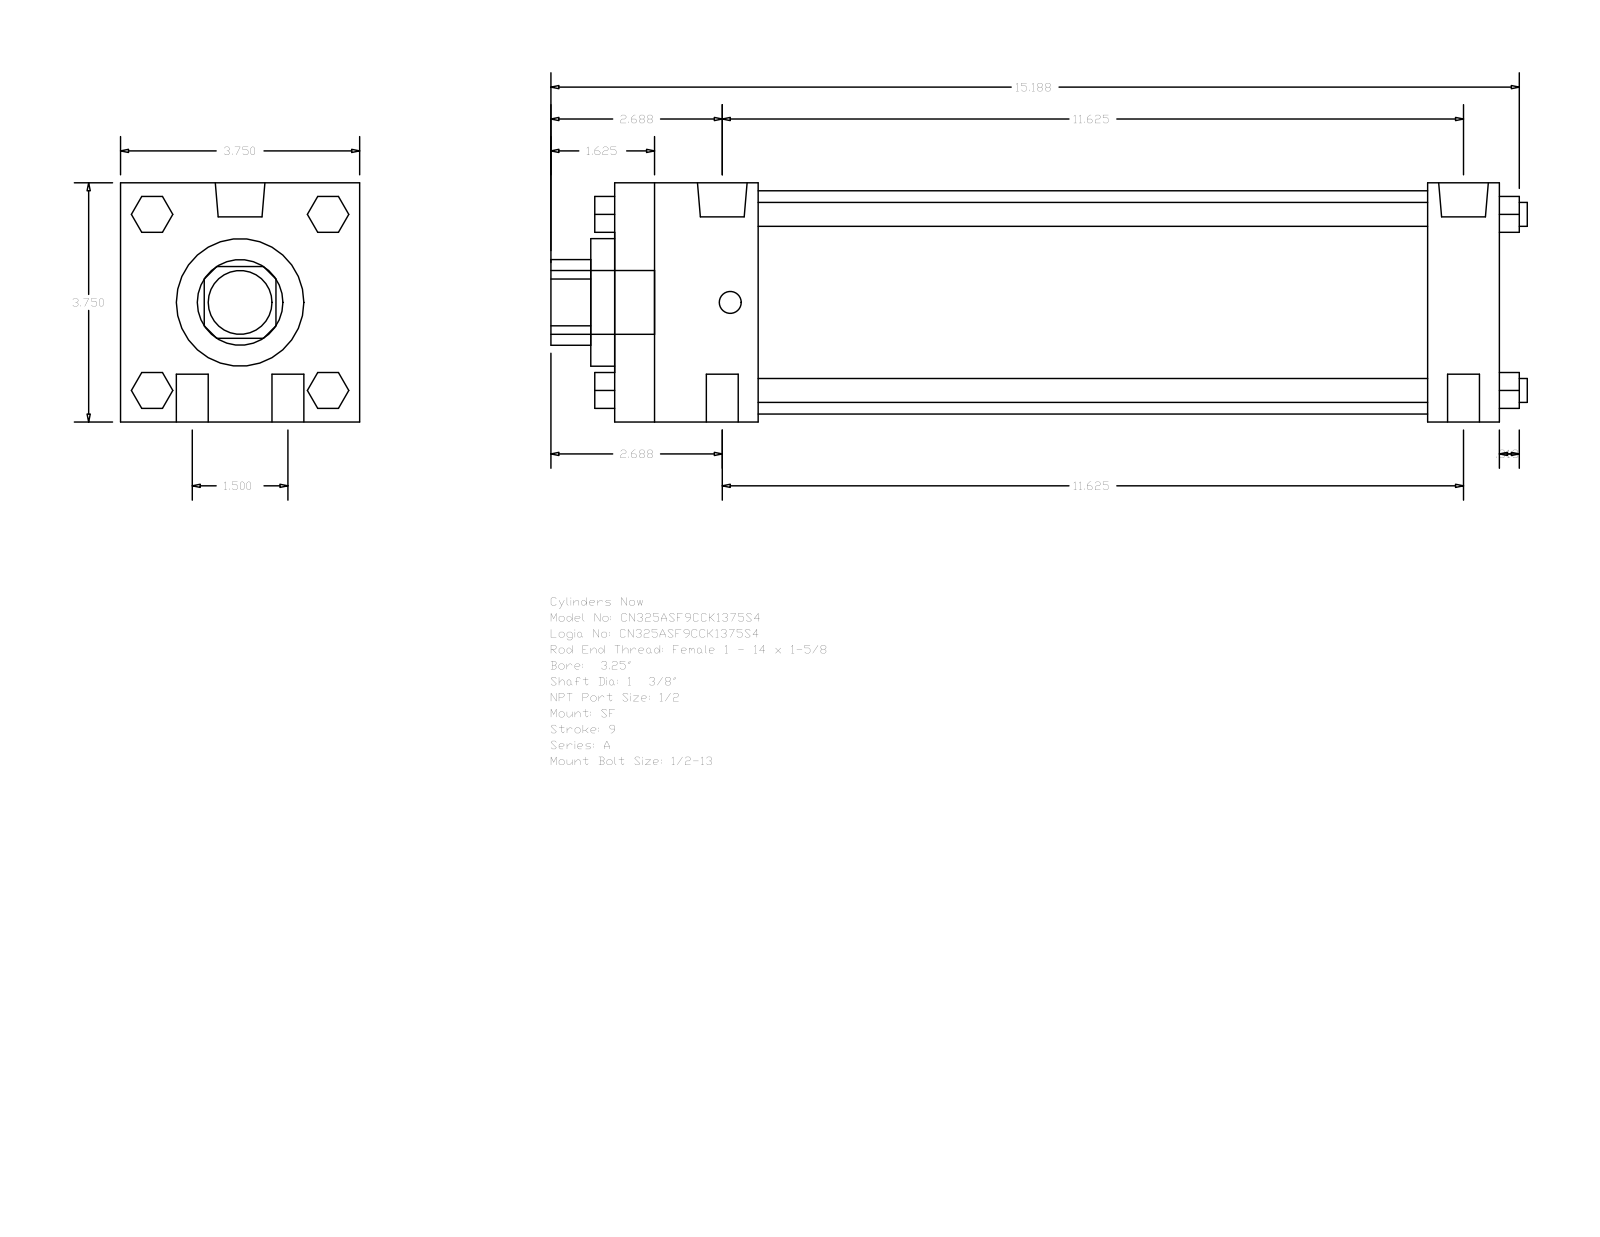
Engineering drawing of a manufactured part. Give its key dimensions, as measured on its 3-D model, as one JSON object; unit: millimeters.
{"part_name": "A_SF__0325_1.375", "step_written_by": "GSSL Pune (CONFIG_CONTROL_DESIGN)", "units": "millimeters", "bodies": {"solids": 0, "faces": 124, "planar": 94, "cylindrical": 30, "other": 0}, "overall_size": [388.94, 95.25, 95.25], "round_holes": [[34.92, 1], [50.8, 1], [88.9, 1]], "round_bosses_or_shafts": [[12.7, 4], [9.53, 4], [19.77, 2], [8.73, 2], [25.4, 1]], "partial_cylinders_radius": [[17.06, 1]], "face_to_face_distances": [95.24, 352.42, 28.57, 323.85, 57.15, 266.7, 295.27, 9.52, 66.67, 333.37]}
